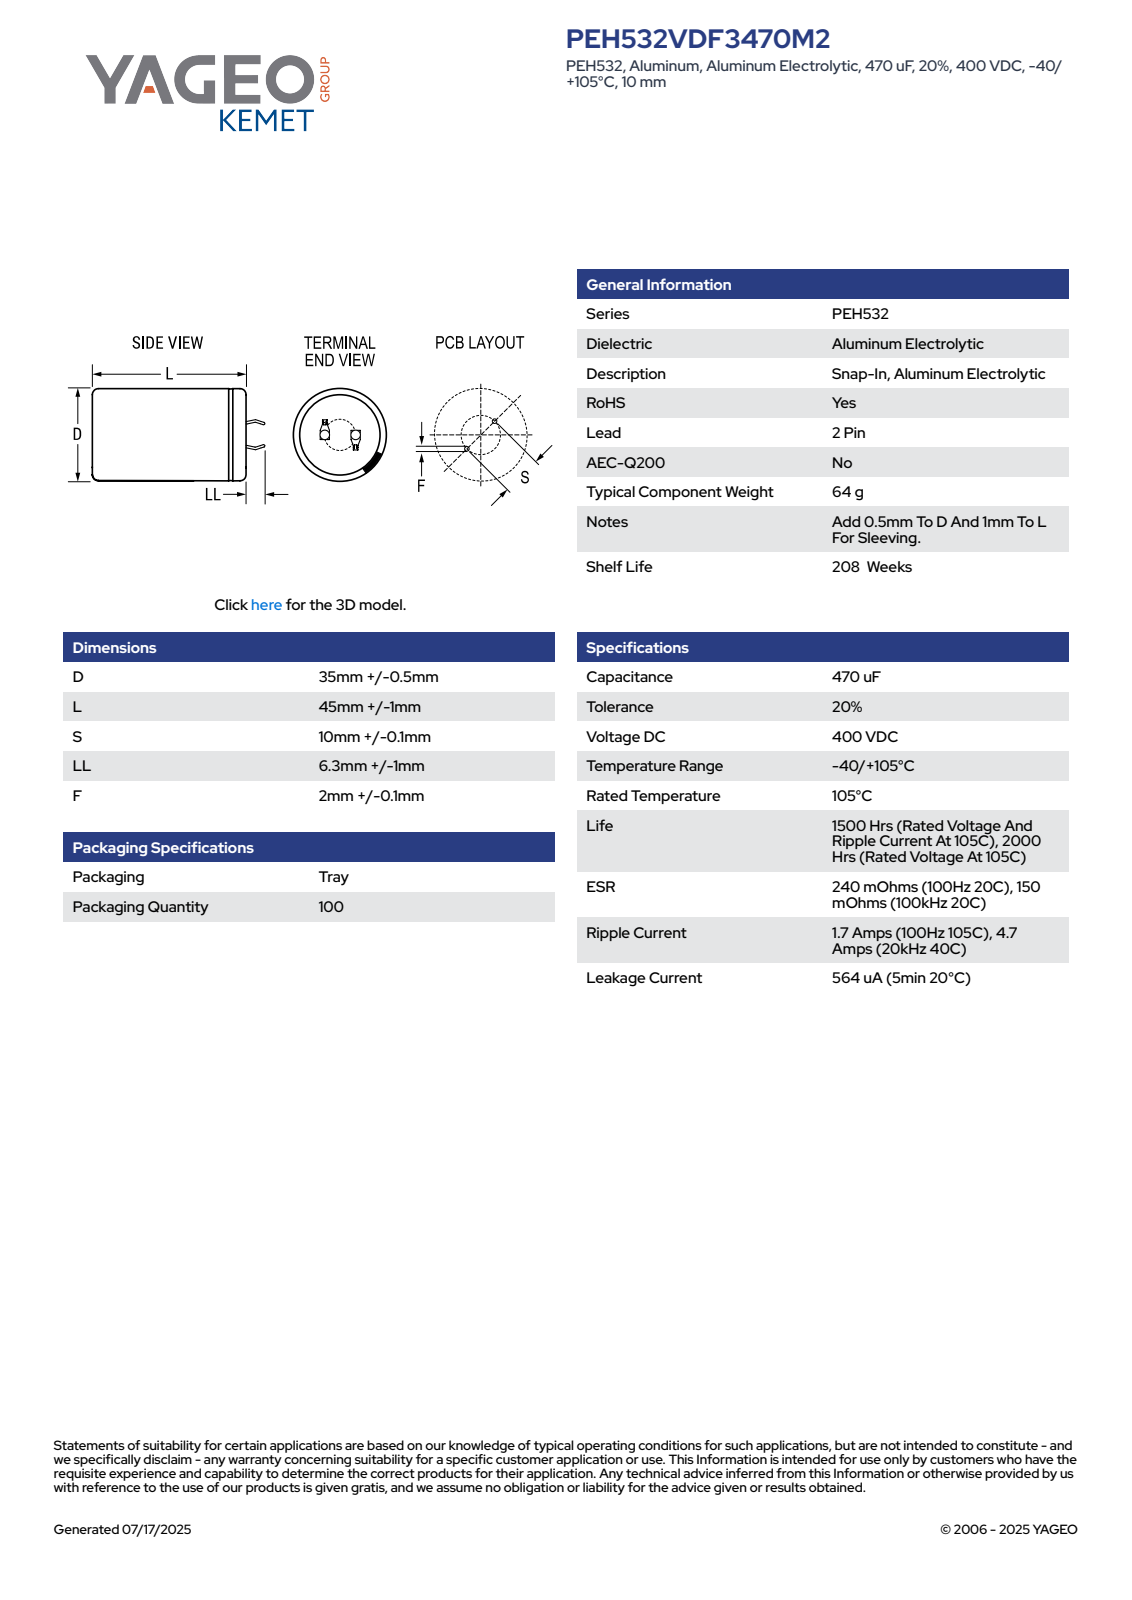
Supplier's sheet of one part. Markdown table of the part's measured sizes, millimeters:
| quantity | value |
| --- | --- |
| part name | CARS_K2P_35X45_D35.5L46S10LL7.3F2.1 |
| STEP written by | SolidWorks 2014 (AUTOMOTIVE_DESIGN) |
| units | millimeters |
| bodies | 1 solid, 100 faces (52 planar, 9 cylindrical, 39 other) |
| overall size | 53.29 × 35.5 × 35.5 |
| volume | 45 025 mm³ |
| surface area | 7 109 mm² |
| round holes (diameter × count) | 31.41 × 1 |
| round bosses / shafts (diameter × count) | 35.5 × 1 |
| partial cylindrical surfaces (radius × count) | 17.74 × 1 |
| main face-to-face distances | 45.99, 0.6, 46.49, 0.5, 7.08, 7.64, 0.75, 1.35, 7.68, 6.48 |
